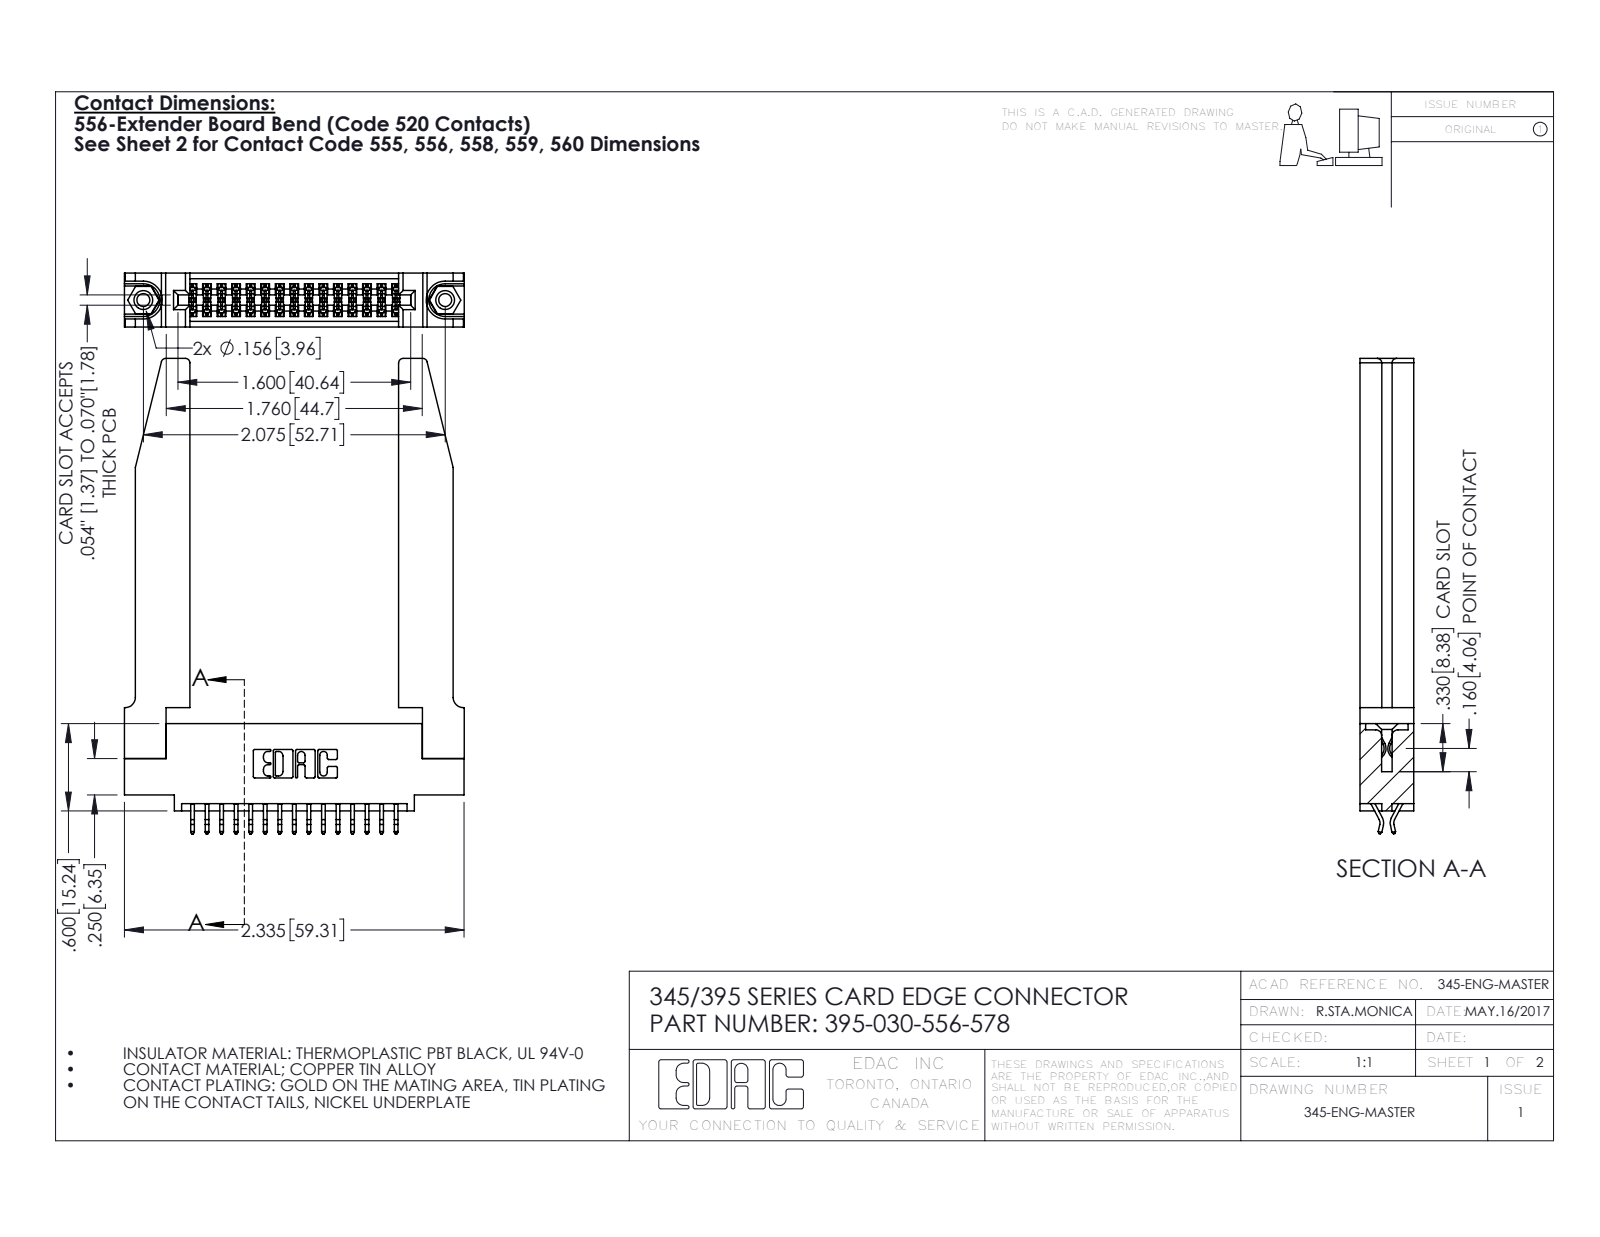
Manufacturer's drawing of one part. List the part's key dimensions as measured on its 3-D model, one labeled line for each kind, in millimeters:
Part name (STEP PRODUCT): 345 Part_0.110 Offset - 0.156 Dia-TH; 345-292-001_556 Tail; 395-030-556-578; 345-220-078_345-220-078 (+1 more)
STEP written by: SolidWorks 2016 (CONFIG_CONTROL_DESIGN)
Units: millimetres
Bodies: 35 solids, 2044 faces (1336 planar, 656 cylindrical, 52 other)
Overall size (bounding box): 83 × 59.3 × 9.4
Volume: 13 200 mm³ · Surface area: 14 420 mm²
Round holes (diameter × count): ⌀2.3 ×2, ⌀3.2 ×2, ⌀4 ×2, ⌀1.6 ×1
Round bosses / shafts (diameter × count): ⌀3.9 ×2
Partial cylindrical surfaces — rounded edges, fillets, slot ends (radius × count): R0.2 ×45, R0.3 ×22, R0.8 ×8, R0.2 ×6, R0.8 ×6, R0.7 ×3, R0.3 ×2, R0.4 ×2
Main face-to-face distances: 9.4, 1.8, 7.6, 3.8, 3.8, 5.1, 0.6, 5.6, 2, 2.5
Hole centre spacings: 6.9, 46.8, 52.7
